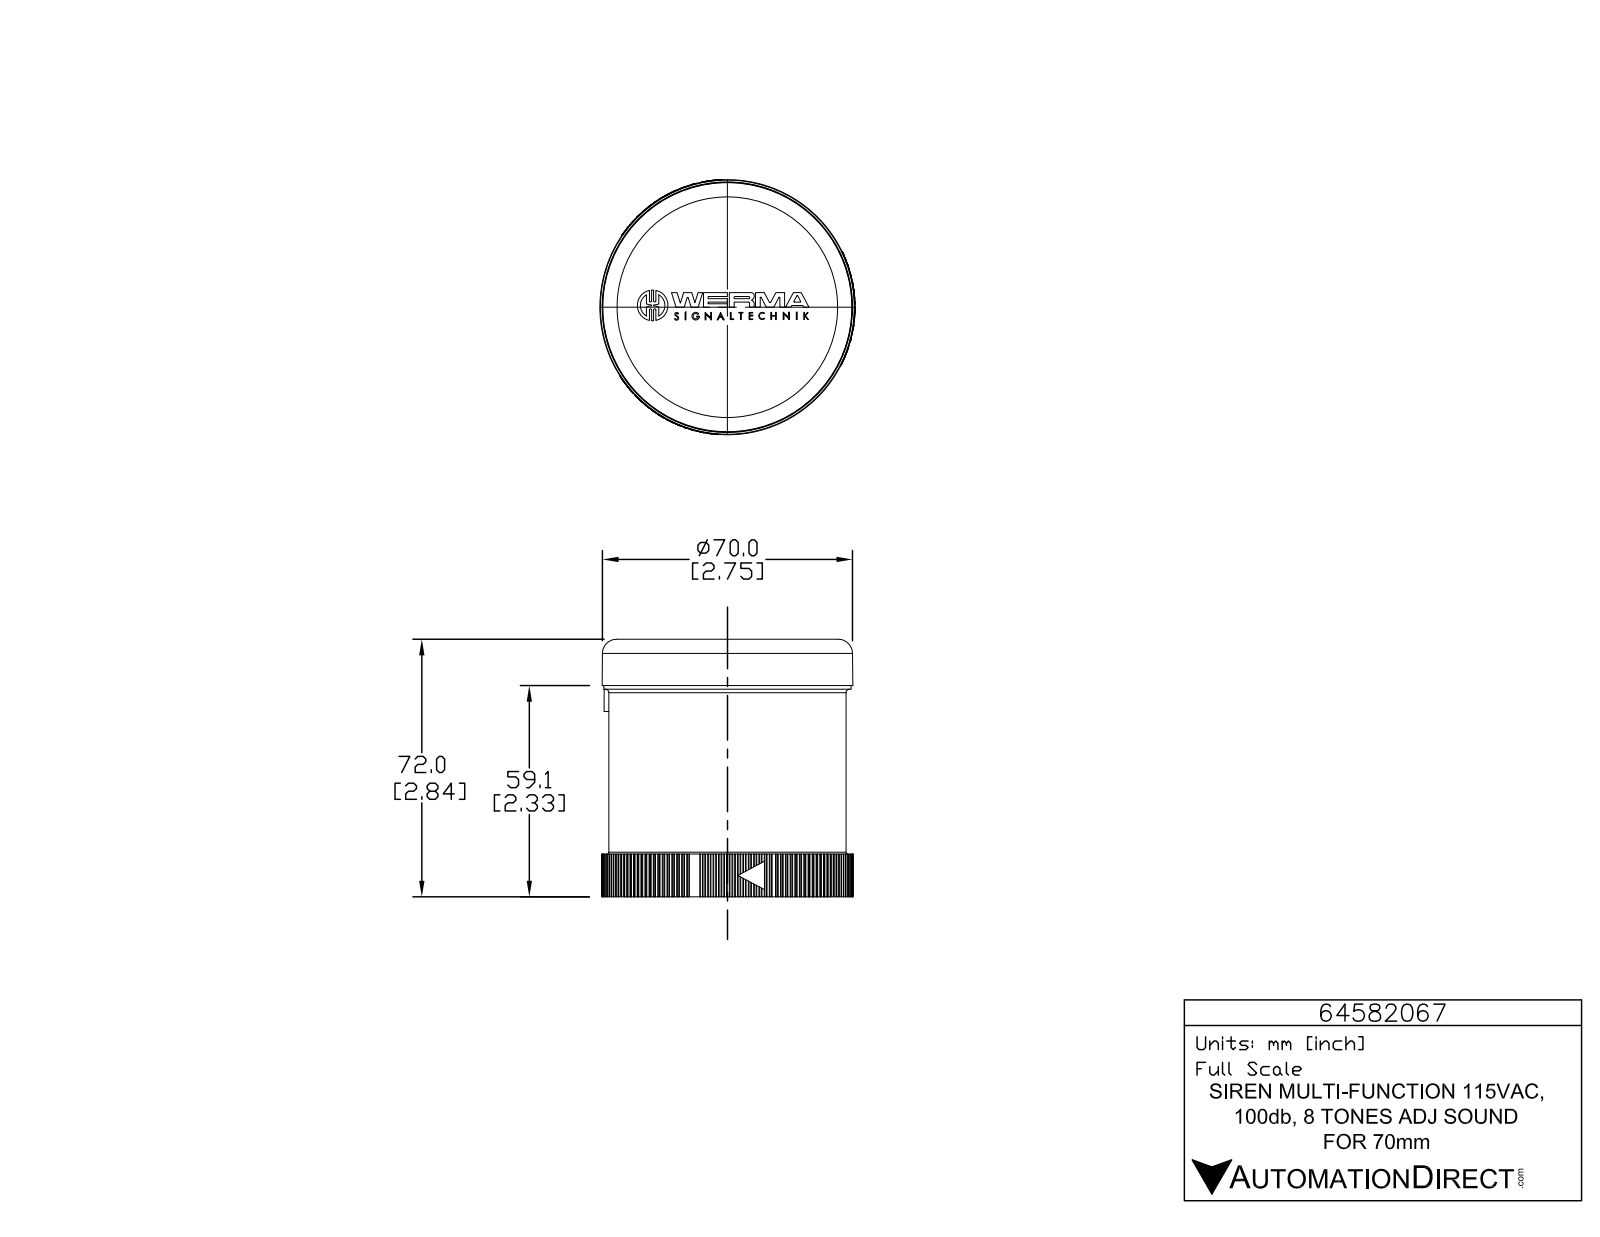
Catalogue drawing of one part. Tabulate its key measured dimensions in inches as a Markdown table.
| quantity | value |
| --- | --- |
| part name | 64582067 |
| STEP written by | SolidWorks 2015 (AUTOMOTIVE_DESIGN) |
| units | inches |
| bodies | 1 solid, 1402 faces (832 planar, 563 cylindrical, 7 other) |
| overall size | 2.762 × 2.762 × 2.705 |
| volume | 13.05 in³ |
| surface area | 38.6 in² |
| round holes (diameter × count) | 0.039 × 3, 2.575 × 1 |
| round bosses / shafts (diameter × count) | 0.226 × 3, 0.056 × 3, 2.762 × 1, 2.717 × 1, 2.606 × 1 |
| partial cylindrical surfaces (radius × count) | 0.008 × 285, 0.008 × 6, 0.008 × 6, 0.008 × 6, 0.131 × 6, 0.004 × 3, 0.005 × 3, 0.008 × 3 |
| main face-to-face distances | 2.327, 2.451, 0.378, 2.705, 2.452, 0.472, 0.094, 2.232, 2.452, 2.452 |
